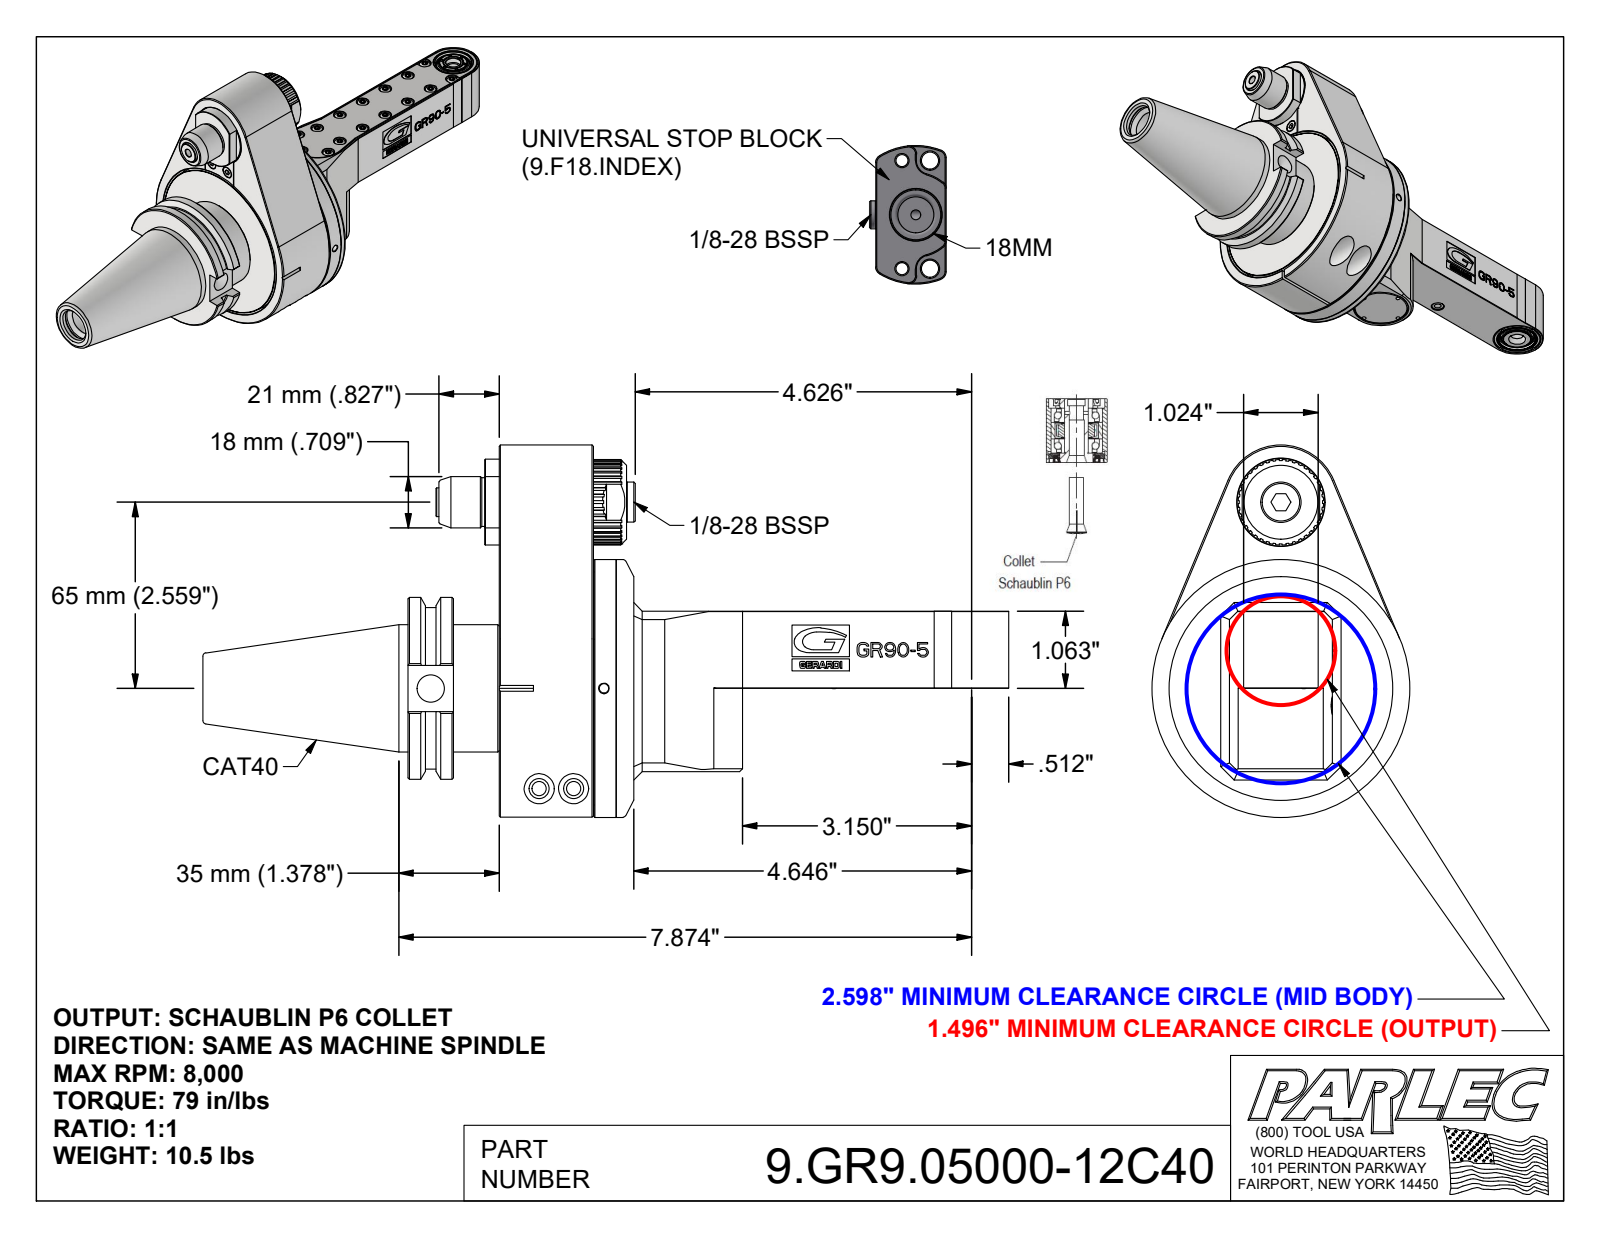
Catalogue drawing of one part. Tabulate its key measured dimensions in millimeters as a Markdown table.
| quantity | value |
| --- | --- |
| part name | 9.GR9.05000-12C40; GR9-5; 9_GA1_446_1 (Classic, Type 1, Cat40, |
| STEP written by | Autodesk Inventor 2025 (AUTOMOTIVE_DESIGN) |
| units | millimeters |
| bodies | 5 solids, 1525 faces (891 planar, 296 cylindrical, 338 other) |
| overall size | 281.4 × 130 × 90 |
| volume | 562 900 mm³ |
| surface area | 130 900 mm² |
| round holes (diameter × count) | 6 × 21, 3.3 × 8, 1.2 × 6, 4.2 × 6, 5 × 6, 2.1 × 4, 4 × 4, 2 × 3, 18 × 3, 6.1 × 2, 7 × 2, 10.5 × 2 |
| round bosses / shafts (diameter × count) | 5.7 × 15, 3 × 7, 10 × 2, 6 × 2, 90 × 1, 78 × 1, 63.5 × 1, 56.4 × 1 |
| partial cylindrical surfaces (radius × count) | 1 × 34, 8 × 5, 9.2 × 5, 2.2 × 2, 3 × 2, 2 × 1, 2.3 × 1, 2.5 × 1 |
| main face-to-face distances | 33, 8, 25, 5, 3, 39, 30, 27, 26, 14 |
| hole center spacings | 11.3, 16, 25.3, 40.8, 32, 37.5, 56.6, 22.6 |
